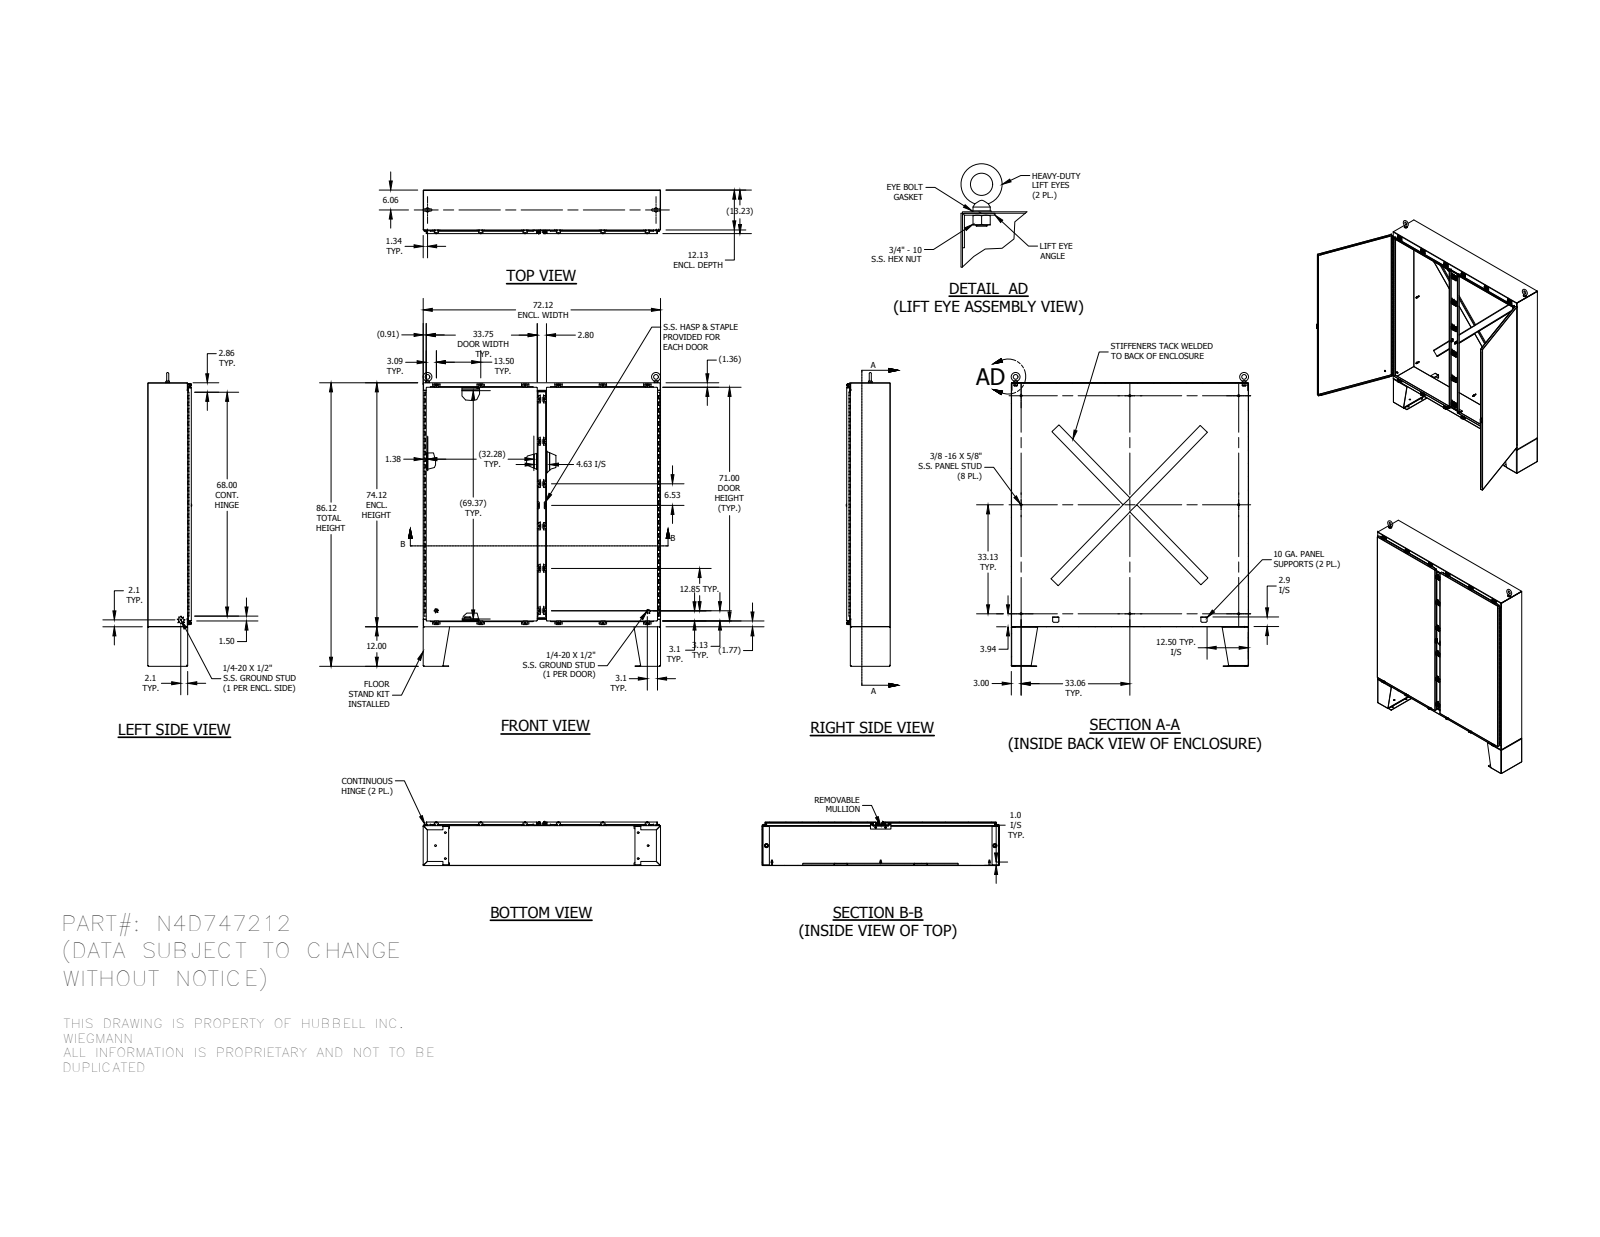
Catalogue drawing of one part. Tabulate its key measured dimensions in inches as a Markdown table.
| quantity | value |
| --- | --- |
| part name | 31666_1; 37218_1; 328131T-68_1; 3032_1 (+8 more) |
| STEP written by | SolidWorks 2014 (AUTOMOTIVE_DESIGN) |
| units | inches |
| bodies | 185 solids, 6996 faces (2802 planar, 2798 cylindrical, 1396 other) |
| overall size | 89.248 × 72.125 × 13.355 |
| volume | 1 663 in³ |
| surface area | 35 257 in² |
| round holes (diameter × count) | 0.11 × 48, 0.211 × 24, 0.281 × 24, 0.3 × 24, 0.563 × 18, 0.375 × 16, 0.196 × 4, 0.201 × 4, 0.312 × 4, 0.313 × 4, 0.142 × 2, 0.156 × 2 |
| round bosses / shafts (diameter × count) | 0.25 × 31, 0.52 × 24, 0.5 × 24, 0.35 × 24, 0.33 × 10, 0.625 × 8, 0.438 × 4, 0.337 × 3 |
| partial cylindrical surfaces (radius × count) | 0.03 × 268, 0.125 × 56, 0.141 × 48, 0.25 × 39, 0.062 × 34, 0.1 × 24, 0.094 × 22, 0.219 × 22 |
| main face-to-face distances | 0.094, 13.133, 13.039, 13.227, 12.031, 1.102, 72.031, 74.031, 12.125, 1.008 |
| hole center spacings | 13.5, 72.977, 0.876, 1.625, 36.314, 37.125, 37.939, 71.717 |
